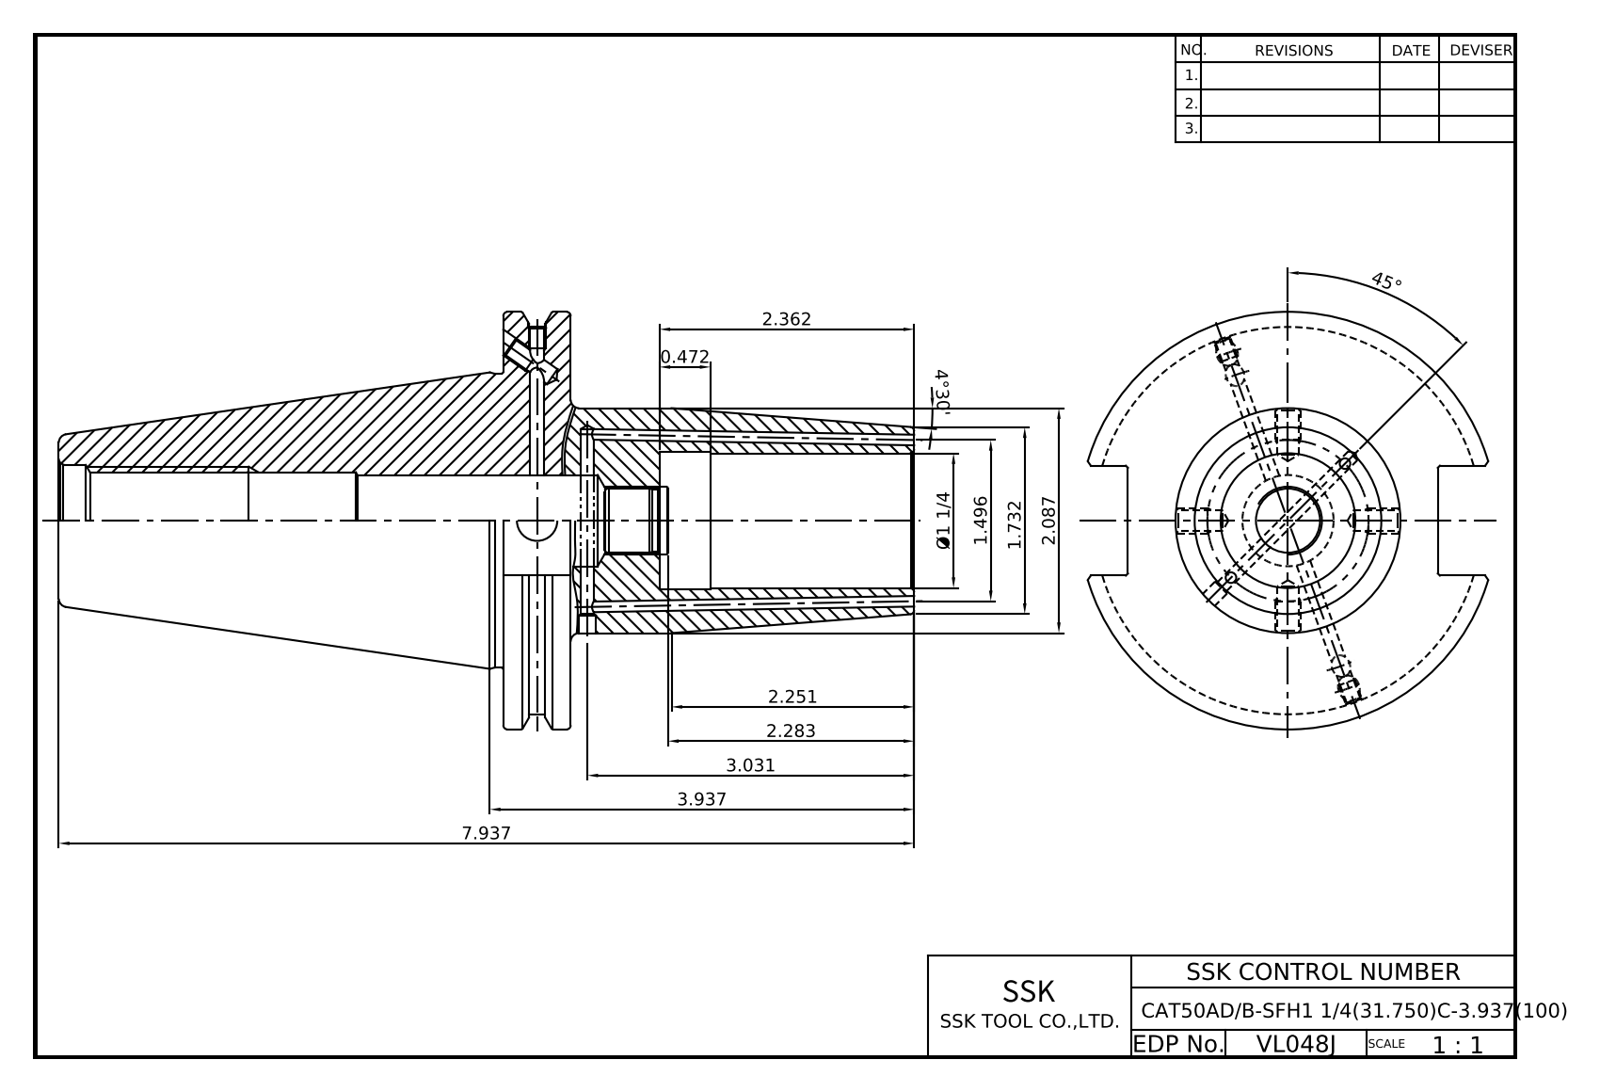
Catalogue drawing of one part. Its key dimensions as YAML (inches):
part_name: "LO-CAT50ADB-SFH31.75C-100"
step_written_by: "Autodesk Inventor 2025 (AUTOMOTIVE_DESIGN)"
units: inches
bodies: {solids: 1, faces: 88, planar: 37, cylindrical: 28, other: 23}
overall_size: [7.937, 3.875, 3.728]
volume: 25.92
surface_area: 100
round_holes:
  - {diameter: 0.079, count: 2}
  - {diameter: 0.128, count: 2}
  - {diameter: 0.163, count: 2}
  - {diameter: 0.165, count: 2}
  - {diameter: 0.197, count: 2}
  - {diameter: 0.375, count: 1}
  - {diameter: 0.587, count: 1}
  - {diameter: 0.865, count: 1}
  - {diameter: 1.031, count: 1}
  - {diameter: 1.25, count: 1}
  - {diameter: 1.297, count: 1}
round_bosses_or_shafts:
  - {diameter: 3.875, count: 1}
  - {diameter: 3.594, count: 1}
  - {diameter: 2.726, count: 1}
  - {diameter: 2.087, count: 1}
face_to_face_distances: [0.625, 1.45, 0.825, 4.125, 4.75, 5.575, 7.937, 3.812, 3.187, 2.362]
